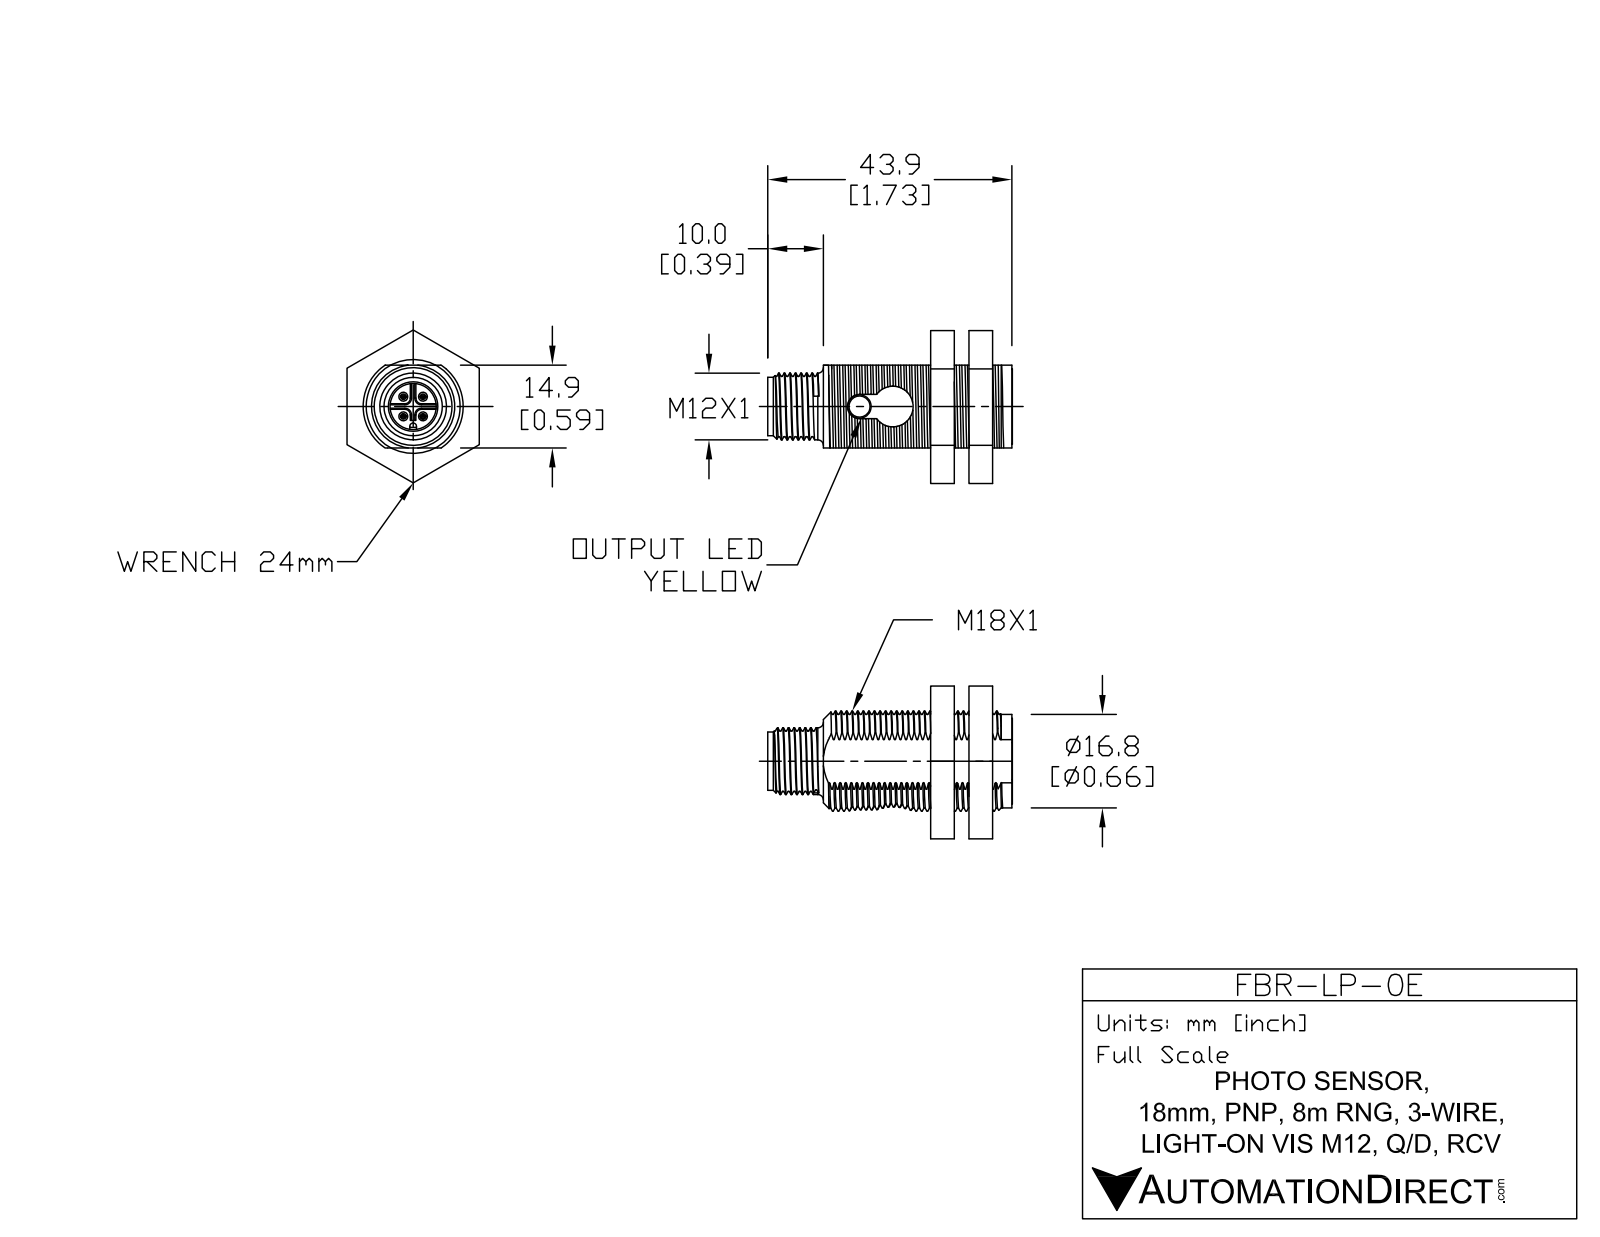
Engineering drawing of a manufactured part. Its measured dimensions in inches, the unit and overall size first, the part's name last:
Units: inches
Overall size (bounding box): 1.728 × 1.09 × 0.967
Round holes (diameter × count): ⌀0.093 ×1, ⌀0.168 ×1, ⌀0.285 ×1, ⌀0.331 ×1
Round bosses / shafts (diameter × count): ⌀0.039 ×4, ⌀0.472 ×1, ⌀0.409 ×1
Partial cylindrical surfaces — rounded edges, fillets, slot ends (radius × count): R0.254 ×2, R0.294 ×2, R0.02 ×1, R0.331 ×1, R0.335 ×1, R0.354 ×1
Main face-to-face distances: 0.315, 0.177, 0.945, 0.591, 0.039, 0.492, 0.138, 0.508, 0.547, 0.193
Hole centre spacings: 0.26
Volume: 0.628 in³ · Surface area: 7.989 in²
Bodies: 7 solids, 215 faces (130 planar, 30 cylindrical, 55 other)
Part name (STEP PRODUCT): FBR-LP-0E
STEP written by: SolidWorks 2011 (AUTOMOTIVE_DESIGN)
